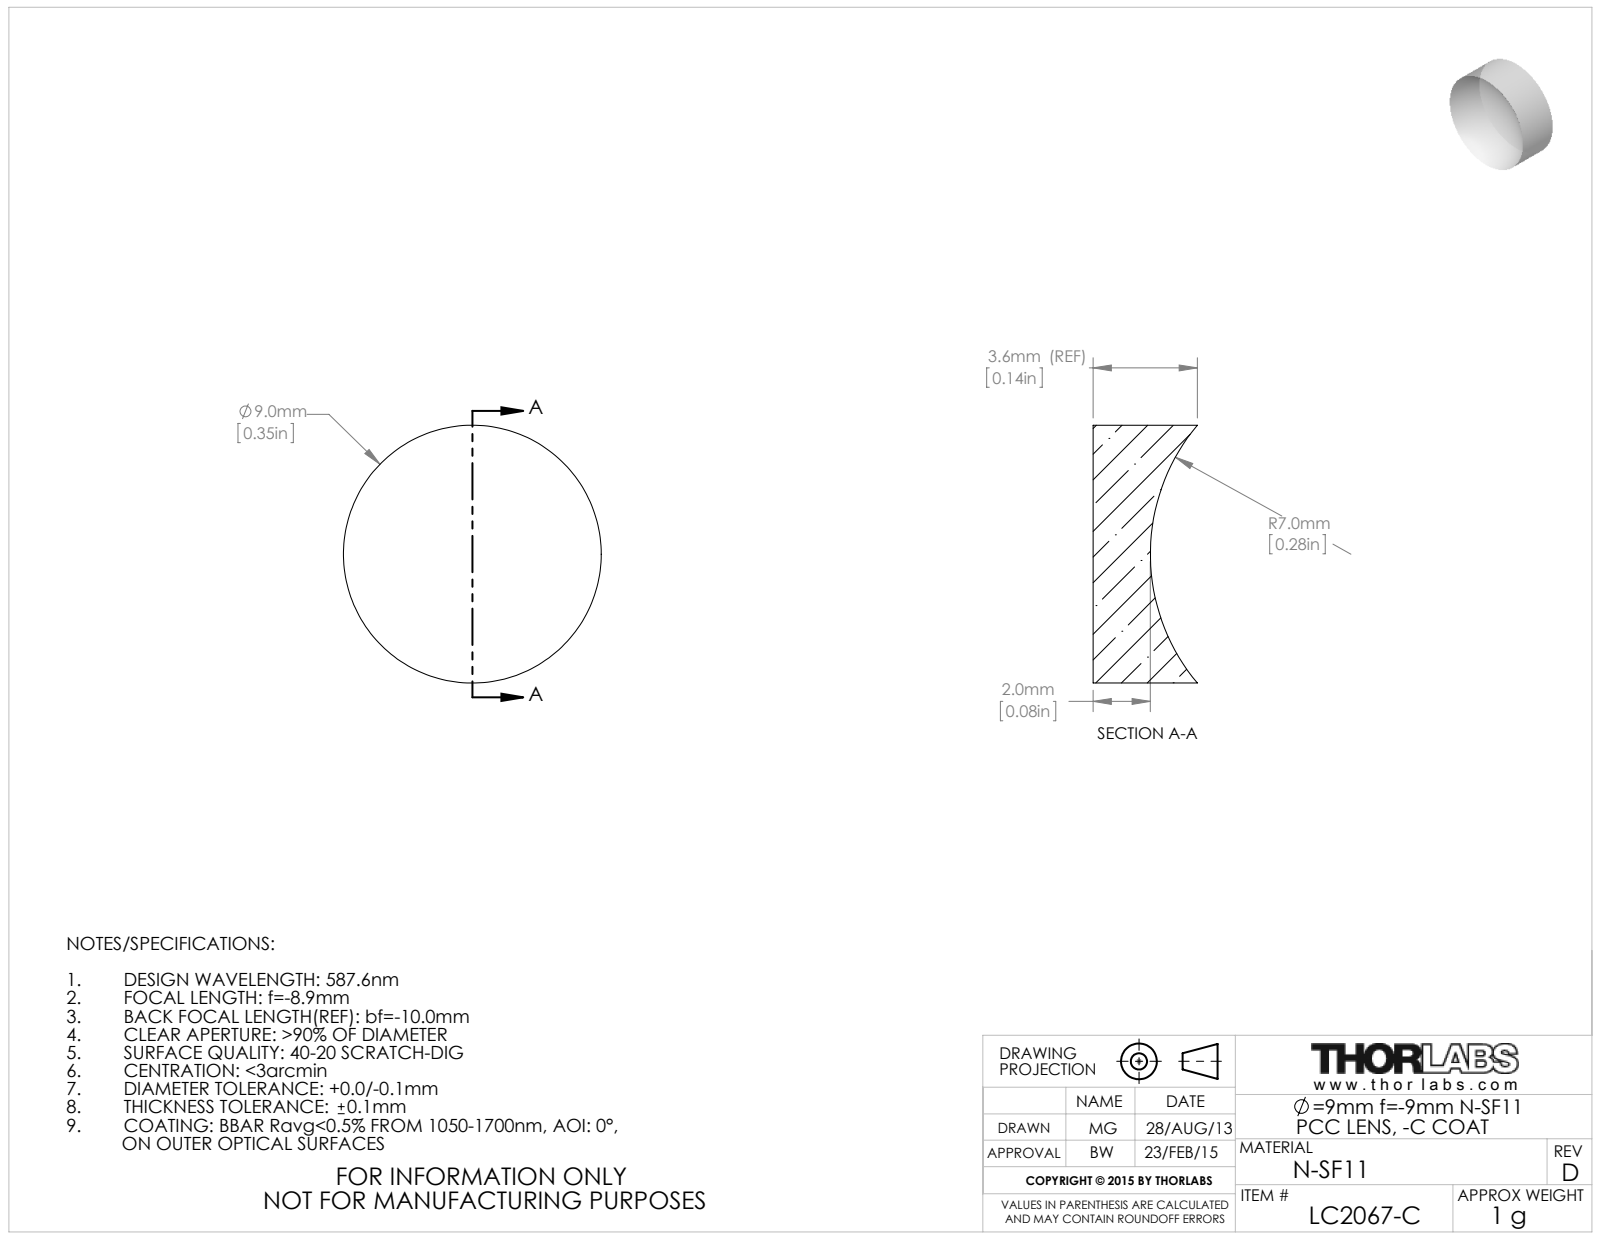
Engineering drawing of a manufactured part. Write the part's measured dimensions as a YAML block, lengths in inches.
part_name: "5434-E0W"
step_written_by: "SolidWorks 2014 (CONFIG_CONTROL_DESIGN)"
units: inches
bodies: {solids: 1, faces: 5, planar: 1, cylindrical: 2, other: 2}
overall_size: [0.354, 0.354, 0.143]
volume: 0.011
surface_area: 0.37
round_bosses_or_shafts:
  - {diameter: 0.354, count: 1}
